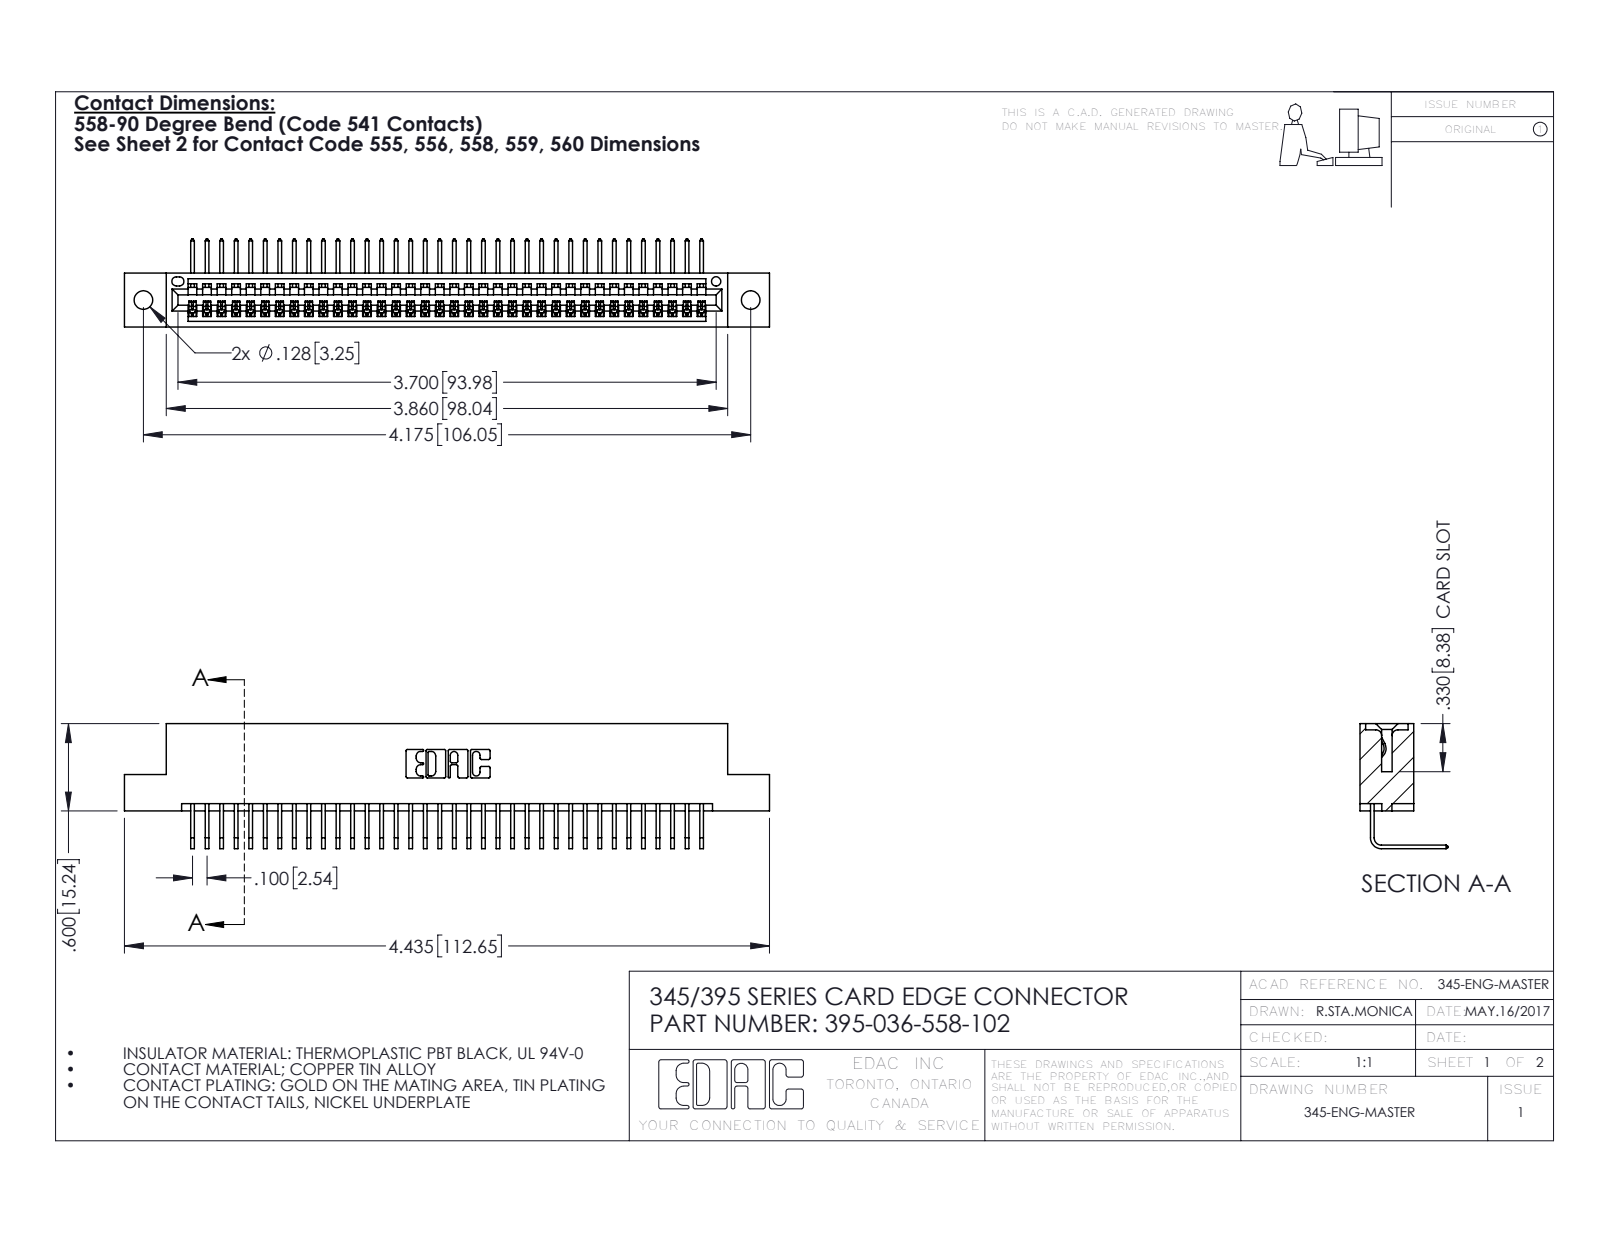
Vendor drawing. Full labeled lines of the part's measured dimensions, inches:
Part name (STEP PRODUCT): 345 Part_Flush Mounting Lugs - 0.128 Dia; 345-292-001_558 Tail - 2; 395-036-558-102
STEP written by: SolidWorks 2016 (CONFIG_CONTROL_DESIGN)
Units: inches
Bodies: 37 solids, 2286 faces (1592 planar, 694 cylindrical, 0 other)
Overall size (bounding box): 4.435 × 0.859 × 0.605
Volume: 0.655 in³ · Surface area: 22.65 in²
Round holes (diameter × count): ⌀0.128 ×2, ⌀0.064 ×1
Partial cylindrical surfaces — rounded edges, fillets, slot ends (radius × count): R0.006 ×72, R0.01 ×22, R0.007 ×6, R0.031 ×6, R0.026 ×3, R0.031 ×2, R0.04 ×2, R0.014 ×1
Main face-to-face distances: 0.298, 0.072, 0.37, 0.2, 0.098, 0.272, 0.025, 0.225, 0.149, 0.072
Hole centre spacings: 0.27, 3.939, 4.175
